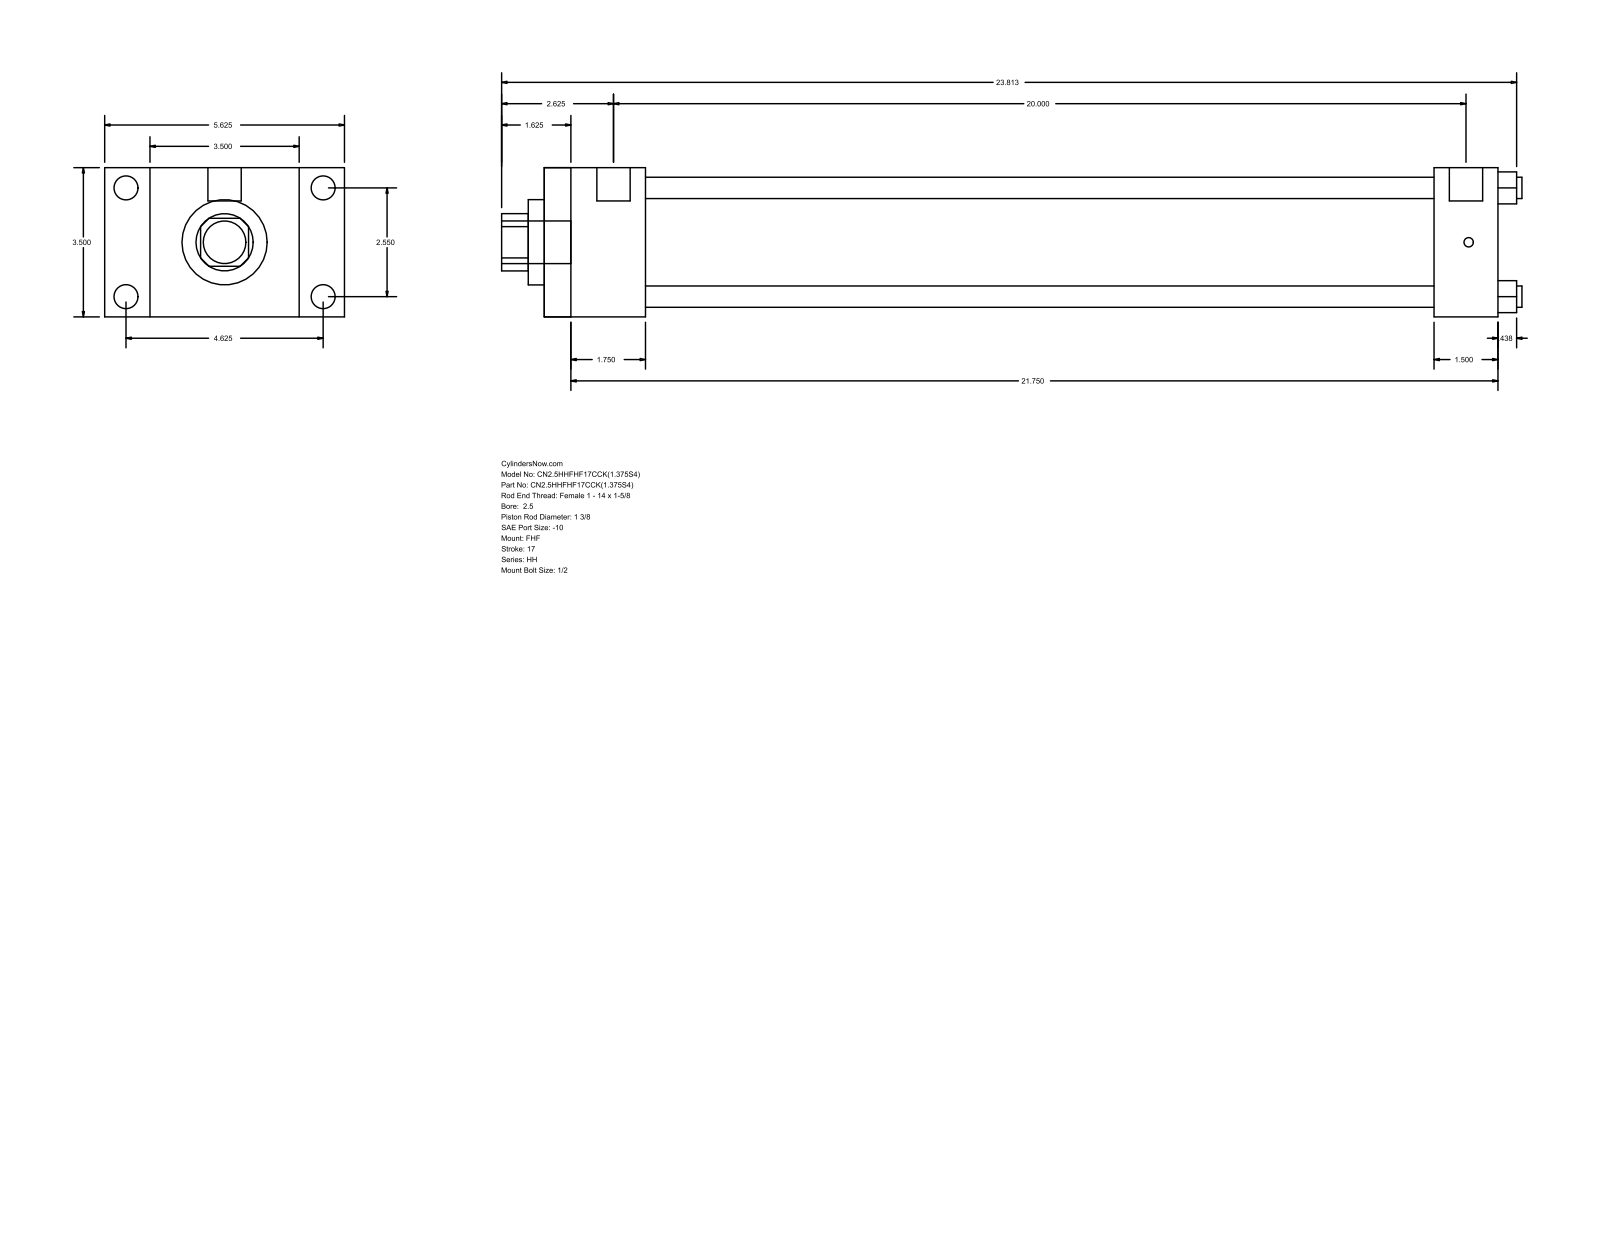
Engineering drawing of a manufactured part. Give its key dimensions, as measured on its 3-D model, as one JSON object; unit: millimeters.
{"part_name": "HH_FHF__0250_1.375", "step_written_by": "GSSL Pune (CONFIG_CONTROL_DESIGN)", "units": "millimeters", "bodies": {"solids": 0, "faces": 88, "planar": 60, "cylindrical": 28, "other": 0}, "overall_size": [608.01, 142.88, 88.9], "round_holes": [[12.7, 4], [34.92, 1], [50.8, 1], [73.03, 1]], "round_bosses_or_shafts": [[14.3, 4], [5.56, 4], [19.84, 2], [25.4, 1]], "partial_cylinders_radius": [[17.06, 1]], "face_to_face_distances": [88.9, 60.32, 26.99, 115.89, 568.33, 508.01, 142.88, 530.22, 469.9, 38.11], "hole_center_spacings": [45.79, 64.76, 91.58]}
